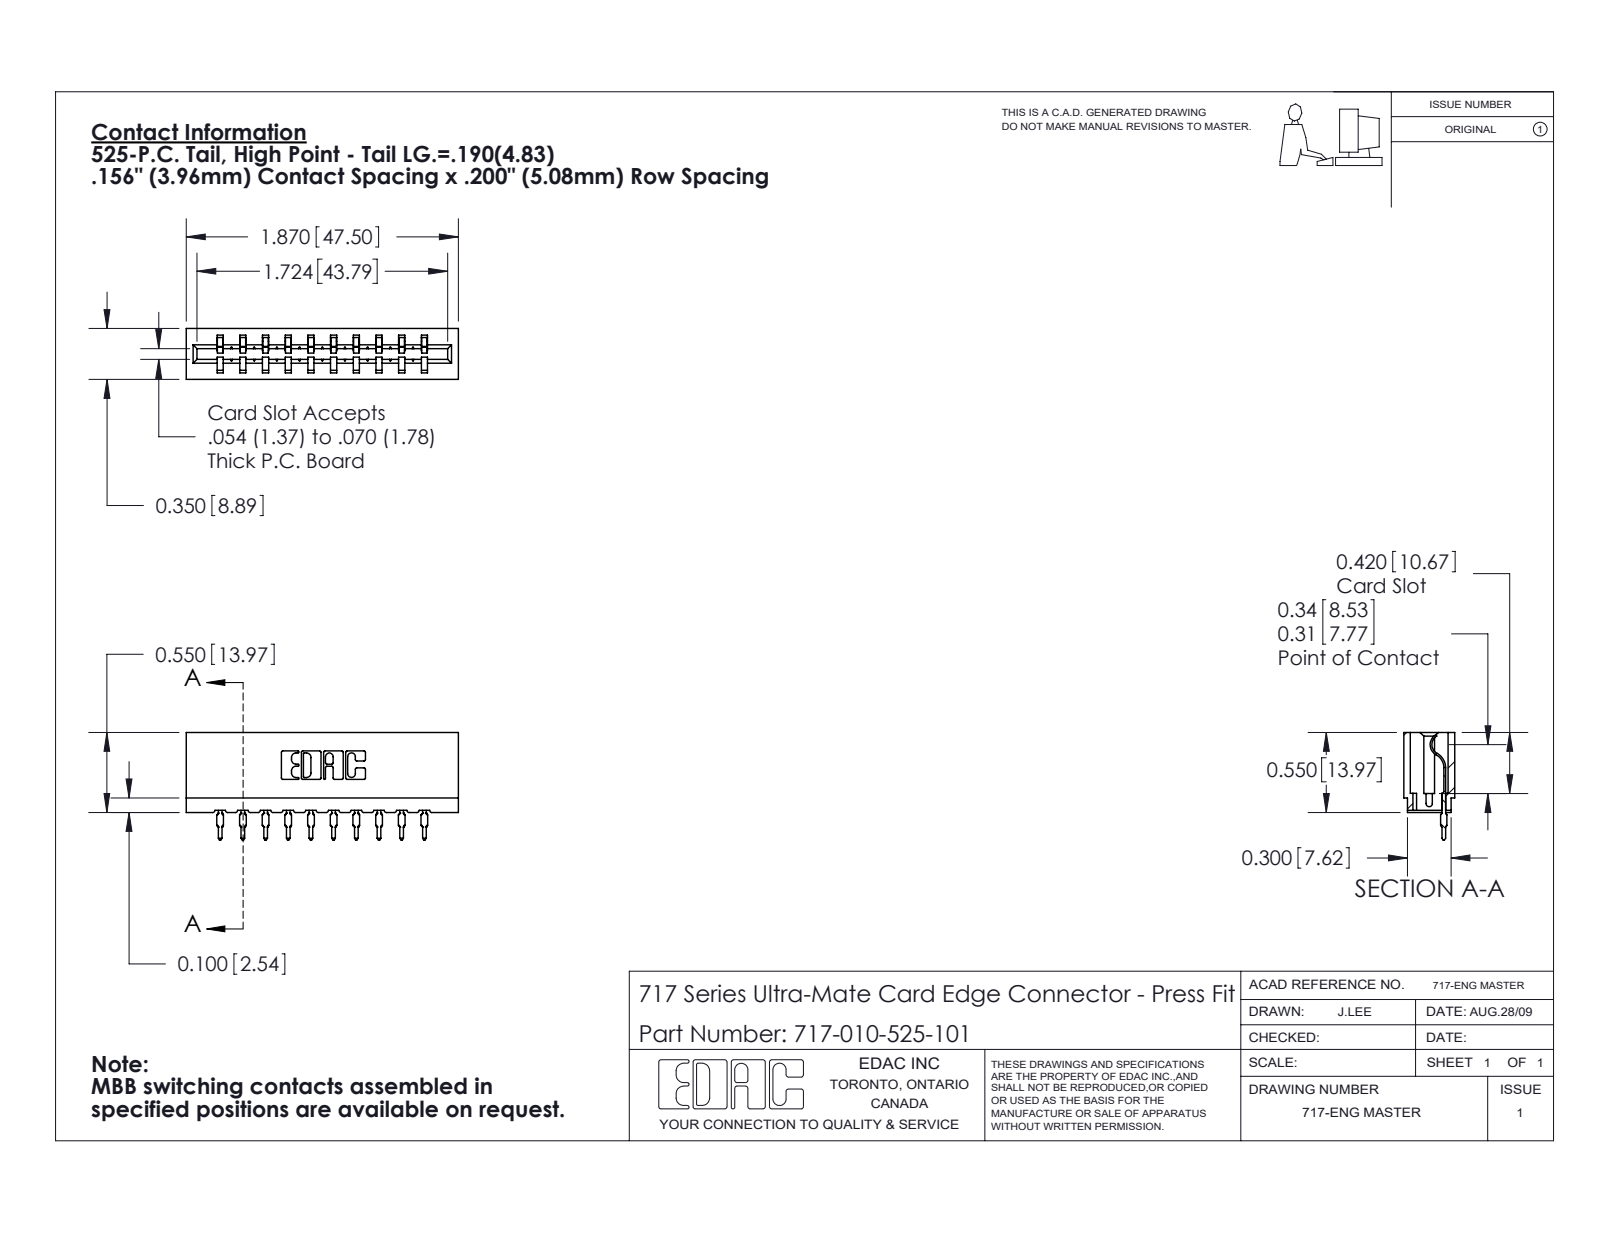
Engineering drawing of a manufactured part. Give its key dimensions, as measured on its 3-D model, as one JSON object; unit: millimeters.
{"part_name": "745-292-001_525; 717-010-525-101; 717 Part_Insulator Option - 06", "step_written_by": "SolidWorks 2020 (CONFIG_CONTROL_DESIGN)", "units": "millimeters", "bodies": {"solids": 11, "faces": 1224, "planar": 734, "cylindrical": 230, "other": 260}, "overall_size": [47.5, 18.8, 8.9], "volume_mm3": 4150, "surface_area_mm2": 5448, "partial_cylinders_radius": [[0.3, 22], [0.4, 20], [0.5, 20], [0.2, 6], [0.8, 6], [0.1, 4], [0.3, 4], [0.7, 3]], "face_to_face_distances": [4, 5.4, 3.5, 15.8, 8.9, 5, 11.9, 7.9, 9, 7.9]}
